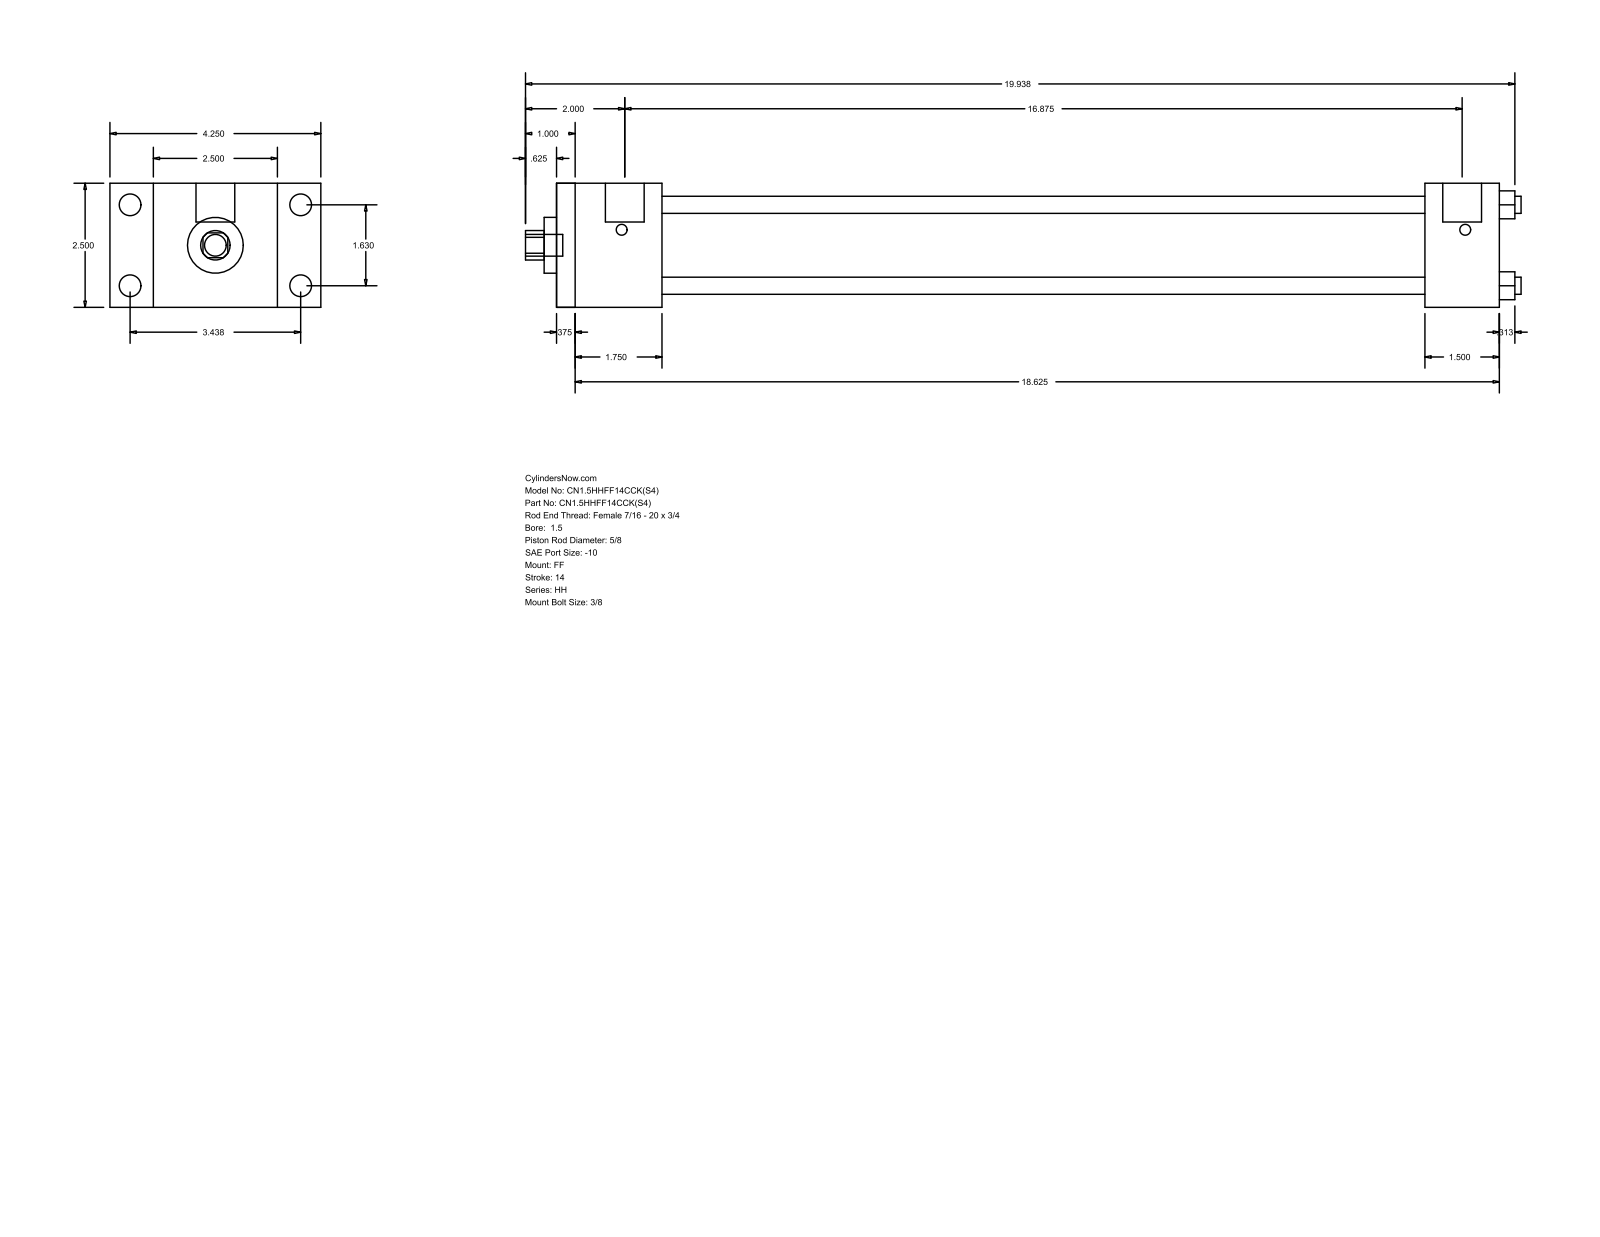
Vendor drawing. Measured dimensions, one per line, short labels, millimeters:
name: HH_FF__0150_0.625
written by: GSSL Pune (CONFIG_CONTROL_DESIGN)
unit: mm
bodies: 0 solids, 92 faces (64 planar, 28 cylindrical, 0 other)
size: 509.59 × 107.95 × 63.5
holes: 4× ⌀8.76, 1× ⌀15.88, 1× ⌀28.57, 1× ⌀44.45
bosses: 4× ⌀11.13, 4× ⌀5.56, 2× ⌀19.84, 1× ⌀11.11
rounds: 1× R7.54
face distances: 63.5, 482.6, 9.52, 38.1, 473.08, 53.97, 44.45, 428.63, 444.5, 434.98
hole spacings: 29.27, 41.4, 58.55
